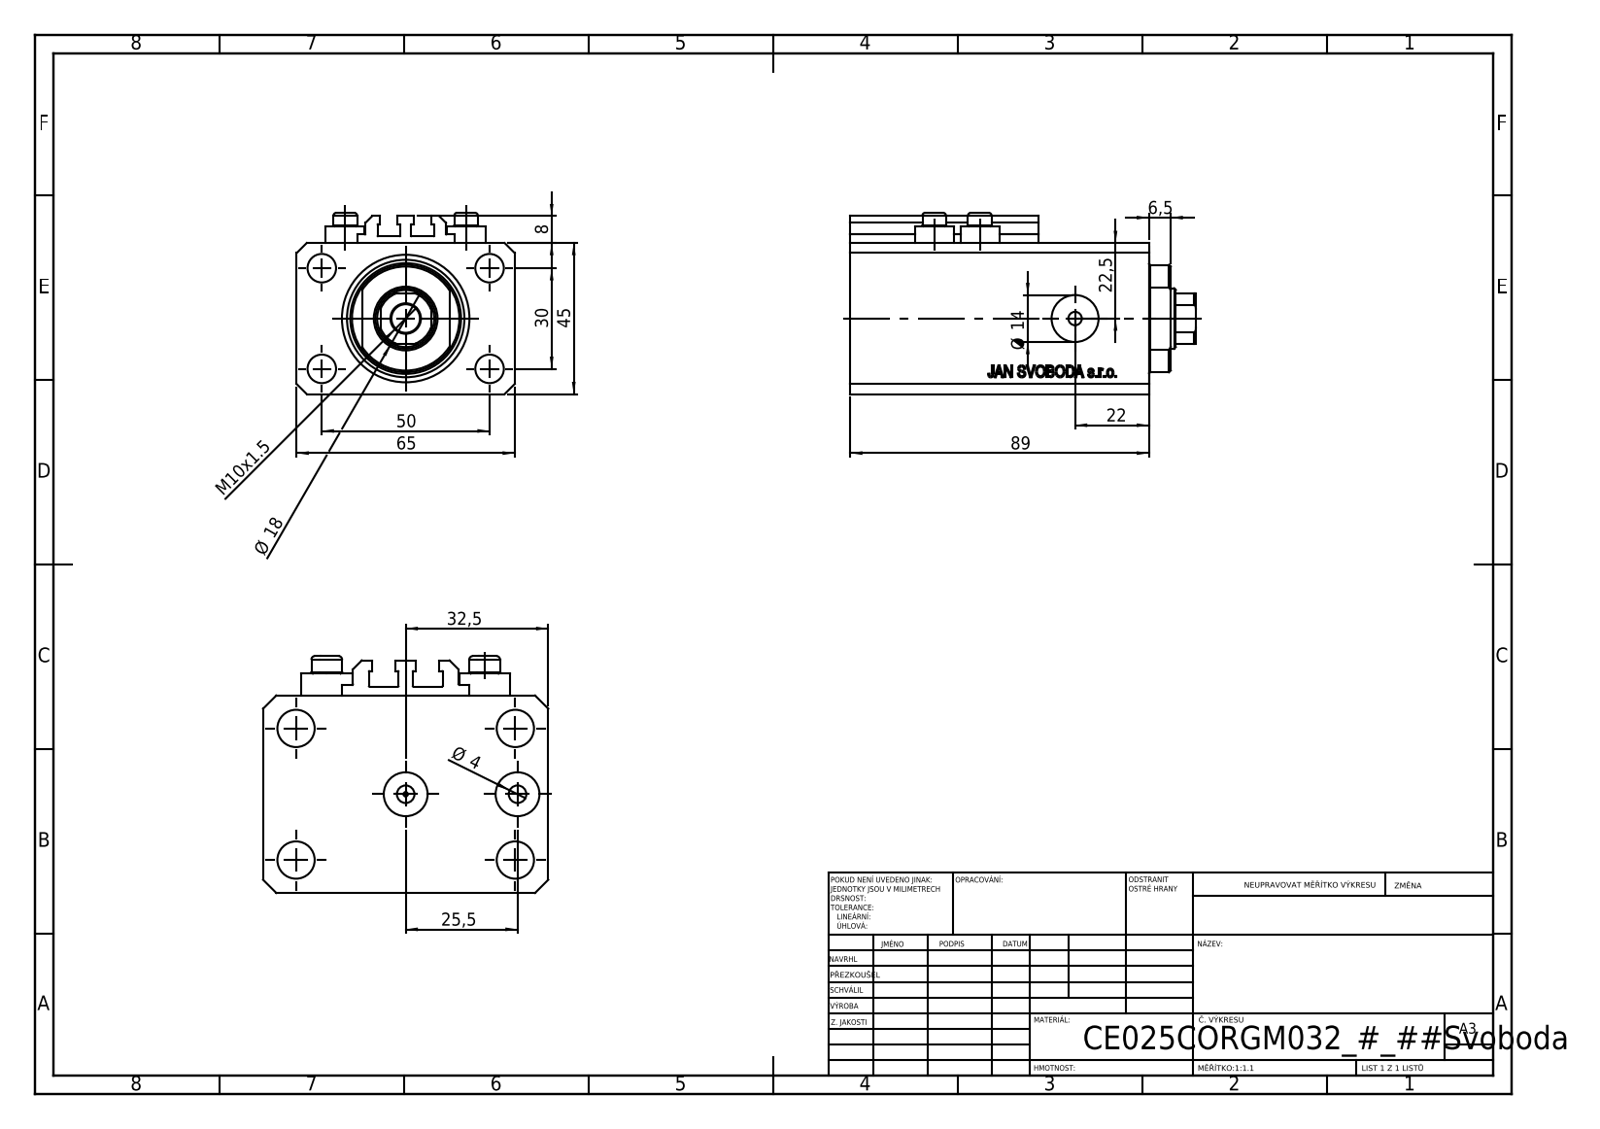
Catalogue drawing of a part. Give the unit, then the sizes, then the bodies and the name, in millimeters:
Units: millimetres
Overall size (bounding box): 103 × 65 × 54
Round holes (diameter × count): ⌀4 ×8, ⌀8.5 ×5, ⌀10 ×2, ⌀14 ×2, ⌀1.25 ×1, ⌀18 ×1, ⌀25 ×1, ⌀38 ×1
Round bosses / shafts (diameter × count): ⌀11.6 ×4, ⌀7 ×4
Partial cylindrical surfaces — rounded edges, fillets, slot ends (radius × count): R0.2 ×10, R8.5 ×1, R16 ×1
Main face-to-face distances: 45, 65, 14, 89, 75, 47, 6.9, 68.1, 82.1, 3
Hole centre spacings: 29.15, 13.6, 15.01, 30, 36, 38.48, 50, 52.68
Volume: 242 317 mm³ · Surface area: 64 368 mm²
Bodies: 8 solids, 1037 faces (503 planar, 88 cylindrical, 446 other)
Part name (STEP PRODUCT): V250CE_VC_C; V250CE_C_VCP; V250CE_C_Body; ALLEN BOLT V250CE
STEP written by: SolidWorks 2019 (CONFIG_CONTROL_DESIGN)
